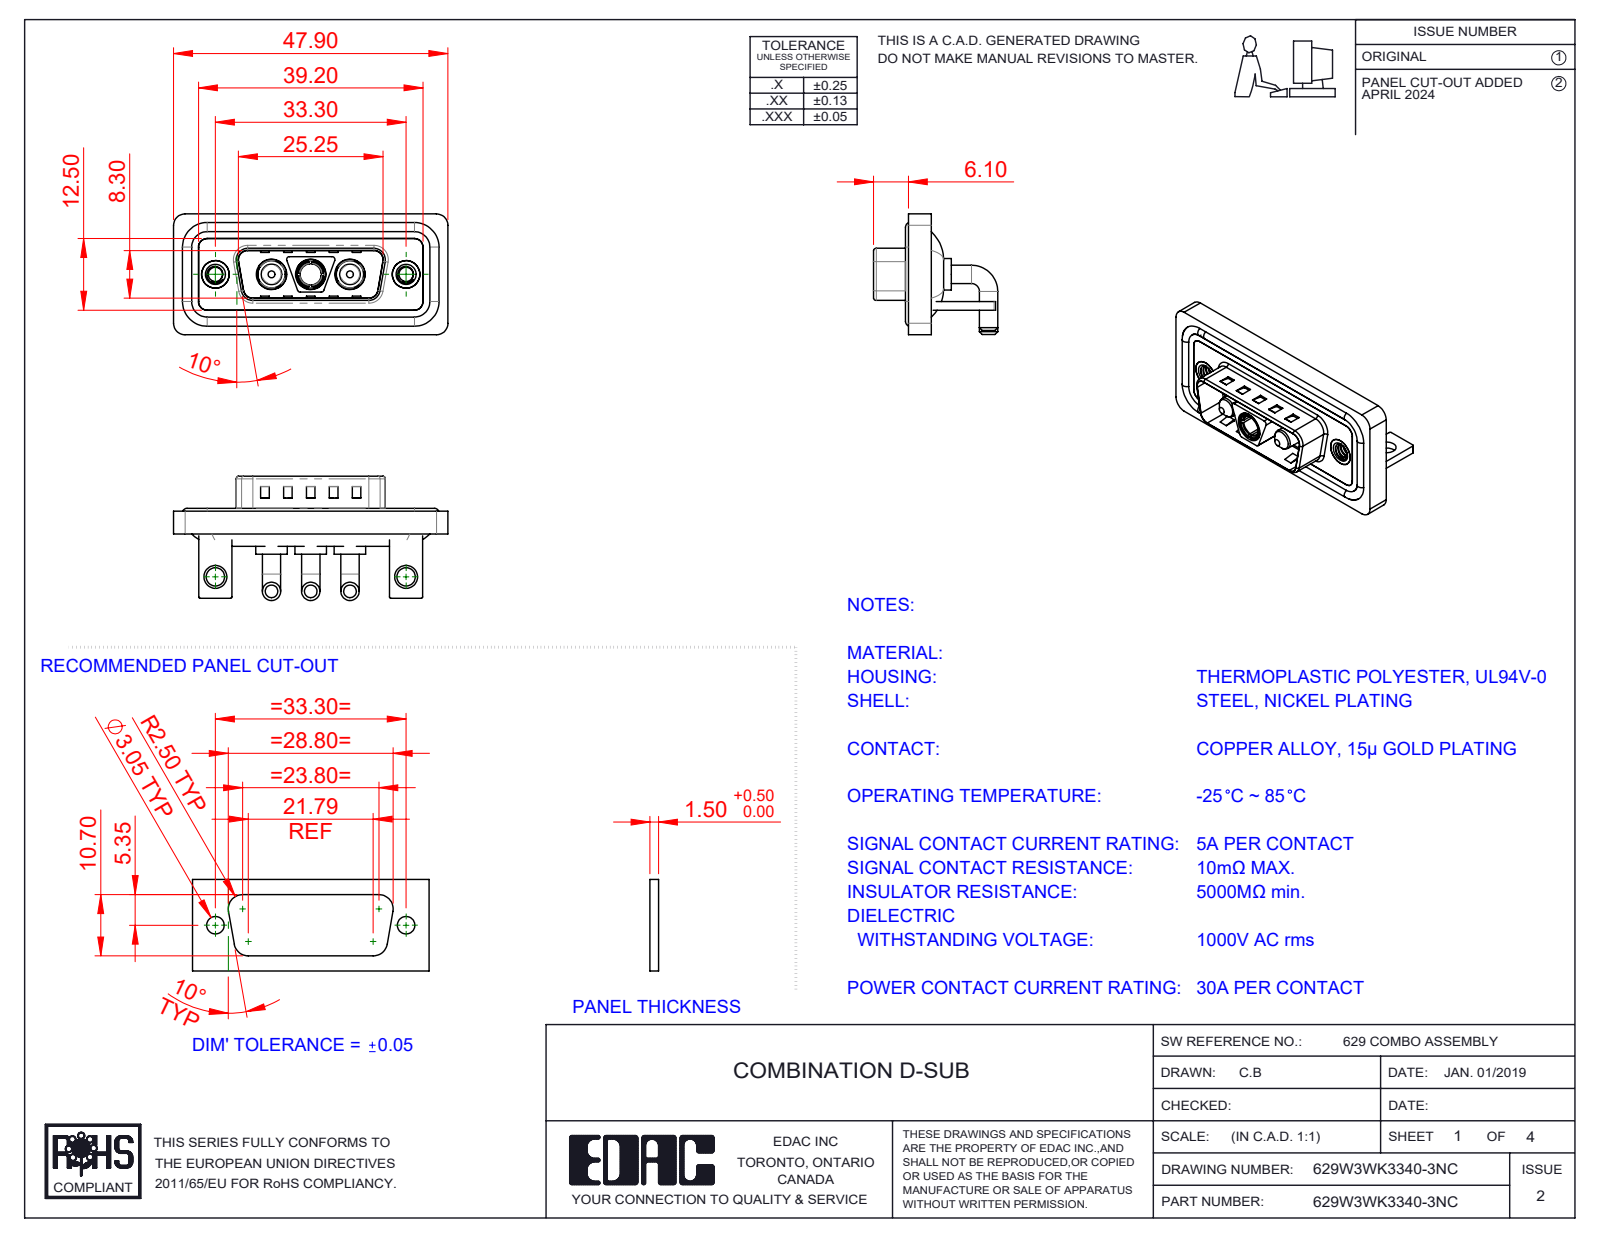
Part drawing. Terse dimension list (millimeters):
name: Power Pin_30A RA; 629Combo Shell Front_15 Contacts; 629Combo Stabilizer Bracket; 629Combo Threaded Rivet_B (+5 more)
written by: SolidWorks 2023 (CONFIG_CONTROL_DESIGN)
unit: mm
bodies: 15 solids, 659 faces (251 planar, 274 cylindrical, 134 other)
size: 47.9 × 21.7 × 21.1
volume: 6 242 mm³; area: 10 060 mm²
holes: 3× ⌀4.85, 3× ⌀5.3, 2× ⌀2.5, 2× ⌀3.2, 2× ⌀4, 2× ⌀4.8, 2× ⌀5, 1× ⌀3.7
bosses: 6× ⌀3.2, 4× ⌀1.6, 3× ⌀5.5, 3× ⌀5.2, 3× ⌀4.75, 3× ⌀3.75, 2× ⌀4.9, 2× ⌀3.6
rounds: 21× R2, 18× R1.5, 16× R0.25, 13× R0.5, 8× R1.6, 4× R0.6, 4× R0.65, 4× R0.9
face distances: 0.4, 1.5, 0.8, 2.9, 1.1, 2.1, 3.7, 1.6, 1.2, 4.5
hole spacings: 6.85, 9.8, 16.65, 23.5, 33.3, 13.7
